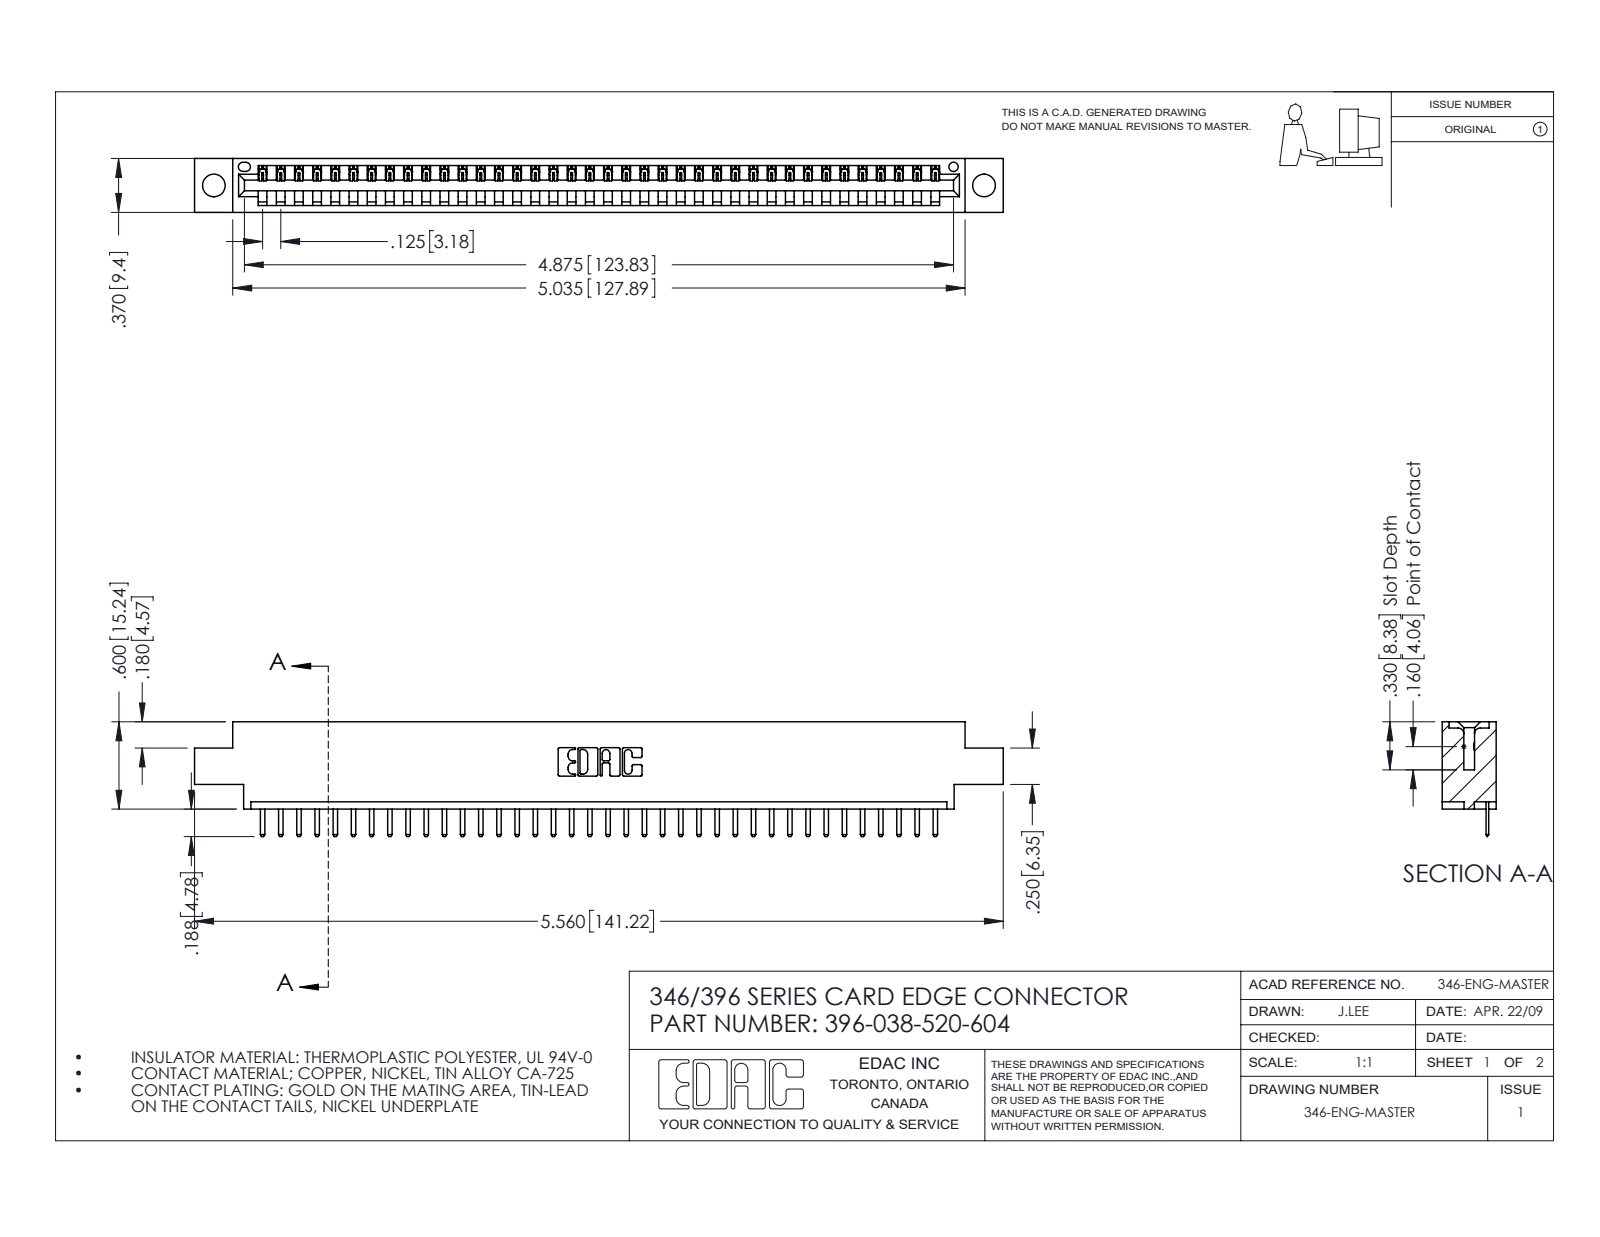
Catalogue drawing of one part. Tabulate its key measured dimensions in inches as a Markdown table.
| quantity | value |
| --- | --- |
| part name | 345-292-001_345-293-120; 346 Part_0.170 Offset - 0.156 Dia-TH; 396-038-520-604 |
| STEP written by | SolidWorks 2016 (CONFIG_CONTROL_DESIGN) |
| units | inches |
| bodies | 39 solids, 2482 faces (1676 planar, 806 cylindrical, 0 other) |
| overall size | 5.56 × 0.788 × 0.37 |
| volume | 0.802 in³ |
| surface area | 24.77 in² |
| round holes (diameter × count) | 0.156 × 2, 0.064 × 1 |
| partial cylindrical surfaces (radius × count) | 0.01 × 78, 0.006 × 76, 0.01 × 22, 0.007 × 6, 0.031 × 6, 0.026 × 3, 0.031 × 2, 0.04 × 2 |
| main face-to-face distances | 0.048, 0.322, 0.37, 0.25, 0.148, 0.222, 0.1, 0.174, 0.072, 0.298 |
| hole center spacings | 0.246, 5.086, 5.295 |
